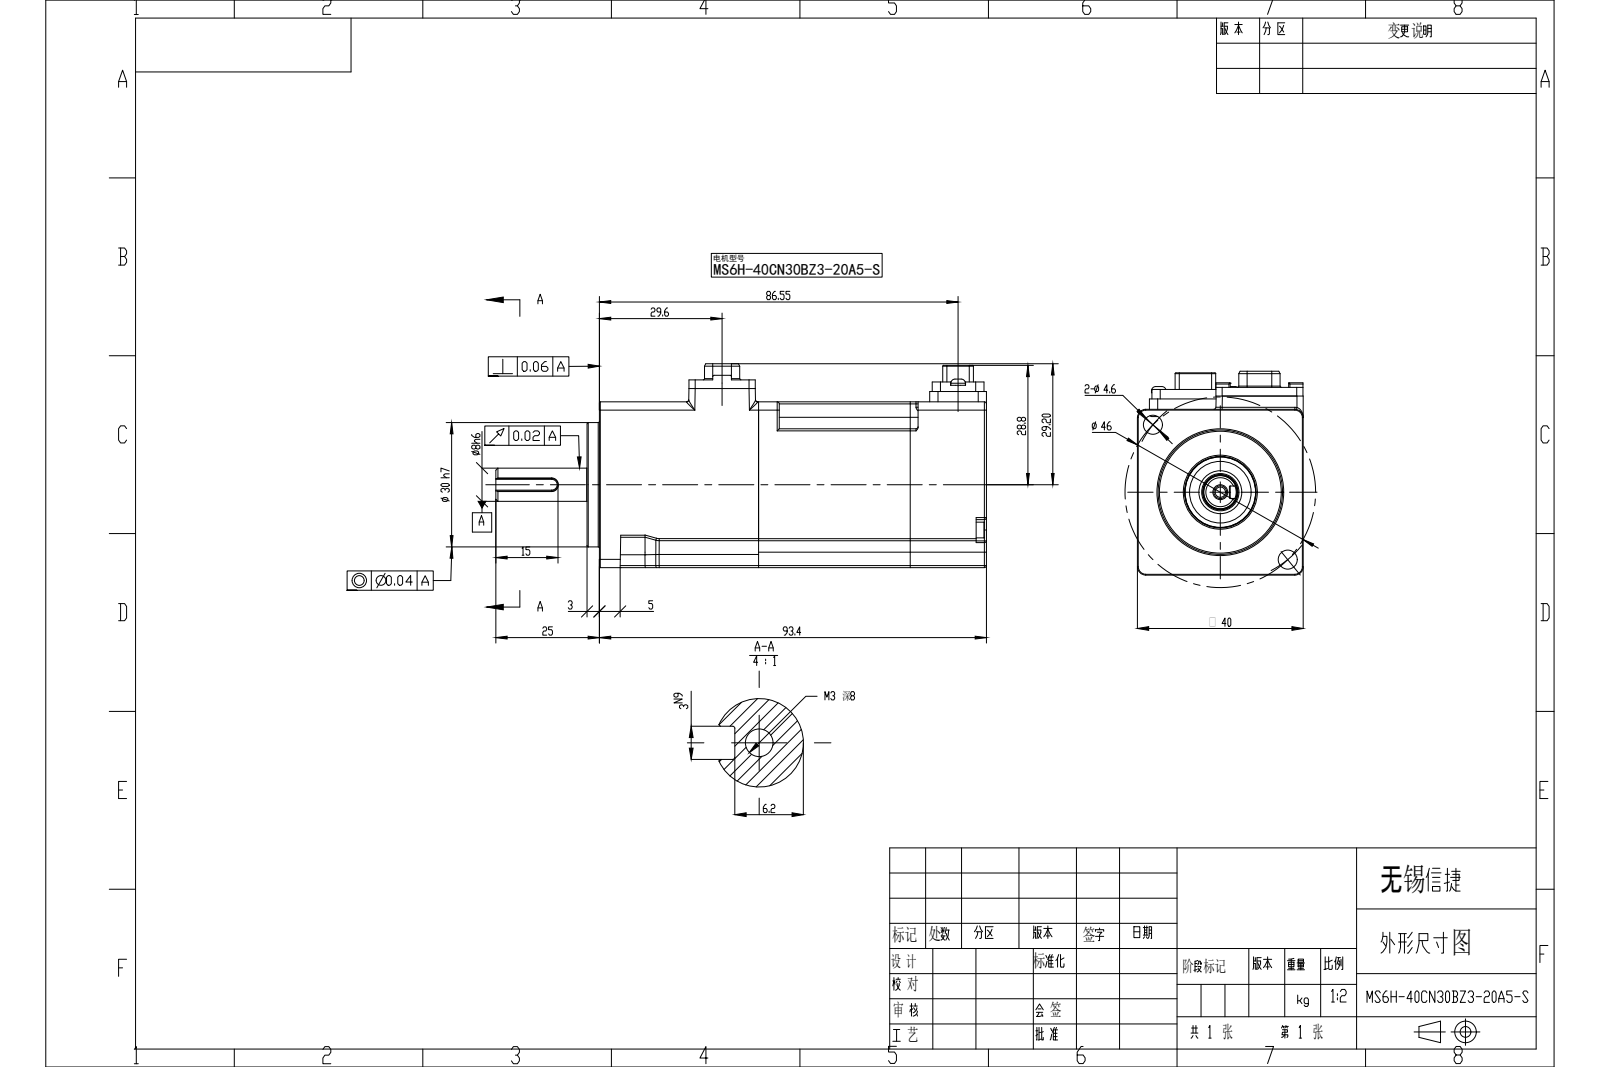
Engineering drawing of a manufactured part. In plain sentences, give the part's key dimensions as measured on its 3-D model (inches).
The part is named "MS6H-40CN30BZ3-20A5-S". Its 3-D file was written by "SolidWorks 2022 (AUTOMOTIVE_DESIGN)". It is 0 solids with 655 faces: 321 planar, 221 cylindrical and 113 other. Overall it measures 4.661 by 1.937 by 1.575 inches. Round holes: 8 of diameter 0.083, 2 of diameter 0.063, 2 of diameter 0.106, 2 of diameter 0.181, 1 of diameter 0.098, 1 of diameter 0.354, 1 of diameter 0.585. Round bosses or shafts: 4 of diameter 0.15, 2 of diameter 0.138, 1 of diameter 1.181, 1 of diameter 0.669, 1 of diameter 0.407, 1 of diameter 0.335, 1 of diameter 0.315. Partial cylindrical surfaces (rounded edges, fillets, slot ends): 66 of radius 0.02, 17 of radius 0.008, 16 of radius 0.079, 10 of radius 0.012, 9 of radius 0.059, 4 of radius 0.039, 4 of radius 0.098, 4 of radius 0.109. The main face-to-face distances are 1.575, 1.319, 0.256, 3.677, 1.063, 0.118, 3.795, 1.63, 1.512, 0.11. The hole center spacings are 0.23, 0.708, 0.906, 1.28, 0.669, 0.315, 0.461, 0.654.
